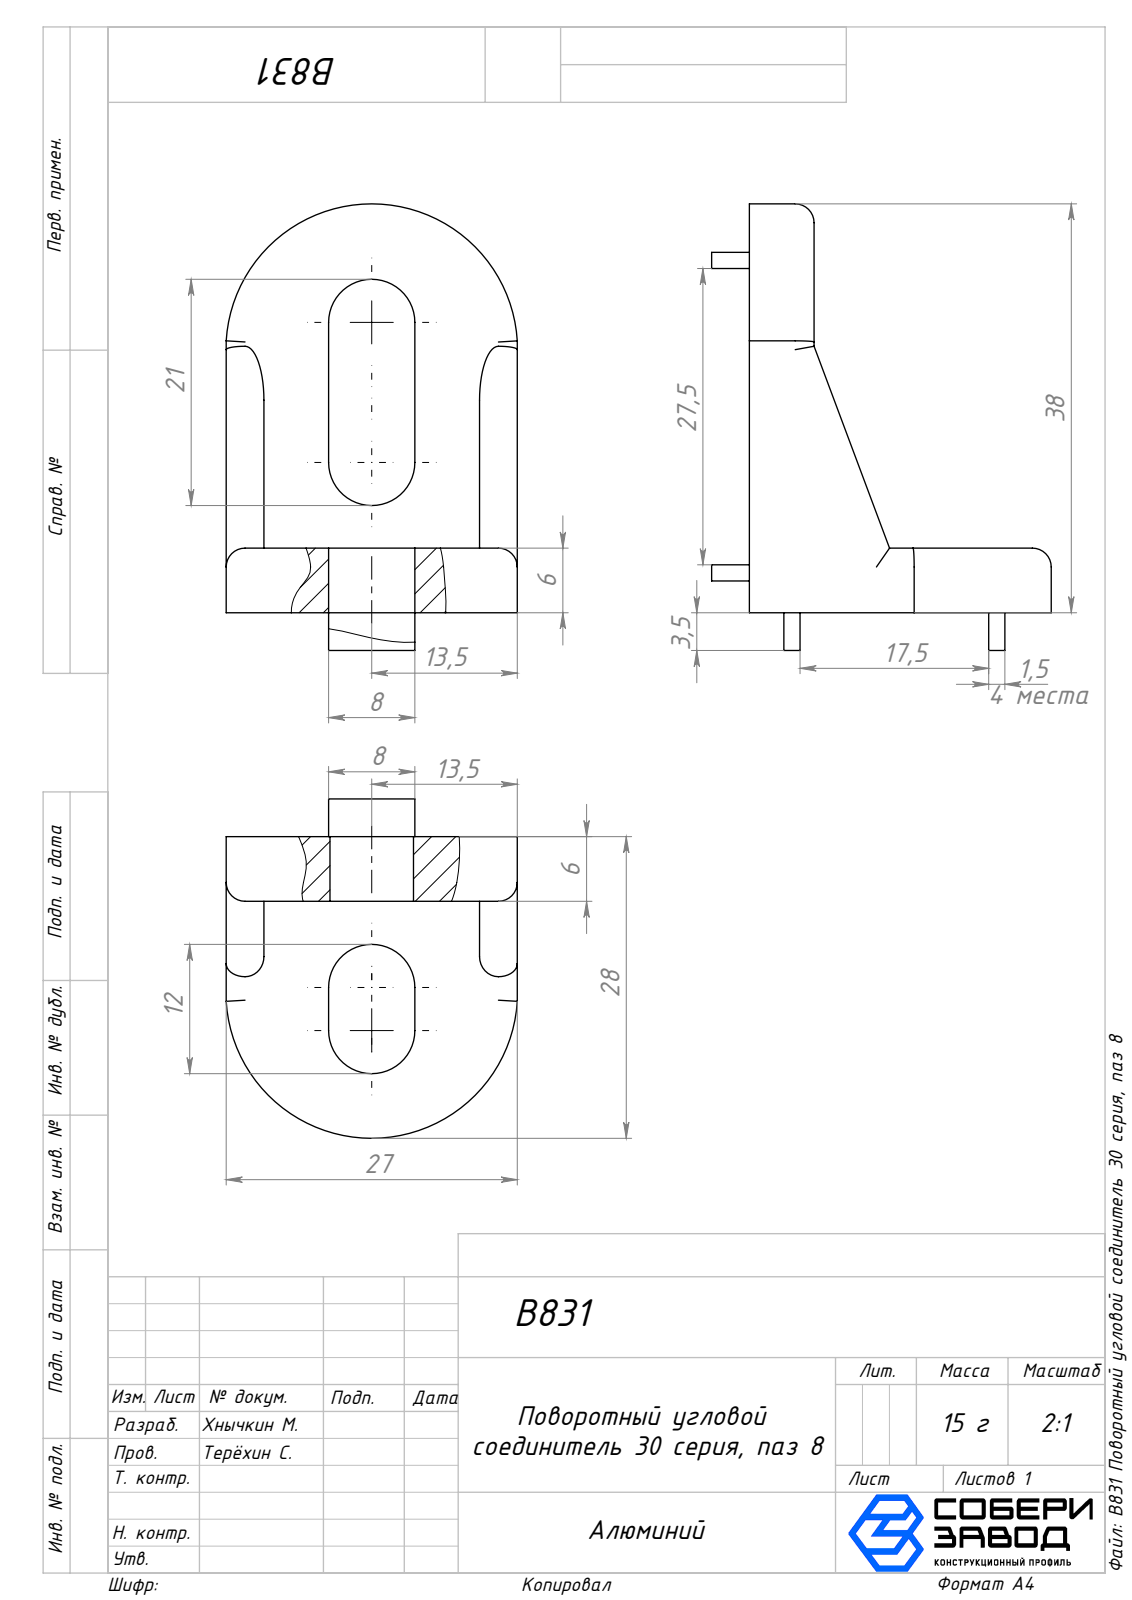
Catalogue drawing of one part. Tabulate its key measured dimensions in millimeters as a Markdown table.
| quantity | value |
| --- | --- |
| part name | B831 Поворотный угловой соединитель 30 серия, паз 8 |
| STEP written by | SolidWorks 2025 (AUTOMOTIVE_DESIGN) |
| units | millimeters |
| bodies | 1 solid, 52 faces (32 planar, 17 cylindrical, 3 other) |
| overall size | 41.45 × 31.5 × 27 |
| volume | 7 878 mm³ |
| surface area | 4 229 mm² |
| partial cylindrical surfaces (radius × count) | 1.75 × 8, 4 × 4, 13.52 × 2 |
| main face-to-face distances | 6, 9.5, 17.5, 27, 8, 3.5, 1.5, 23.5, 14, 19 |
